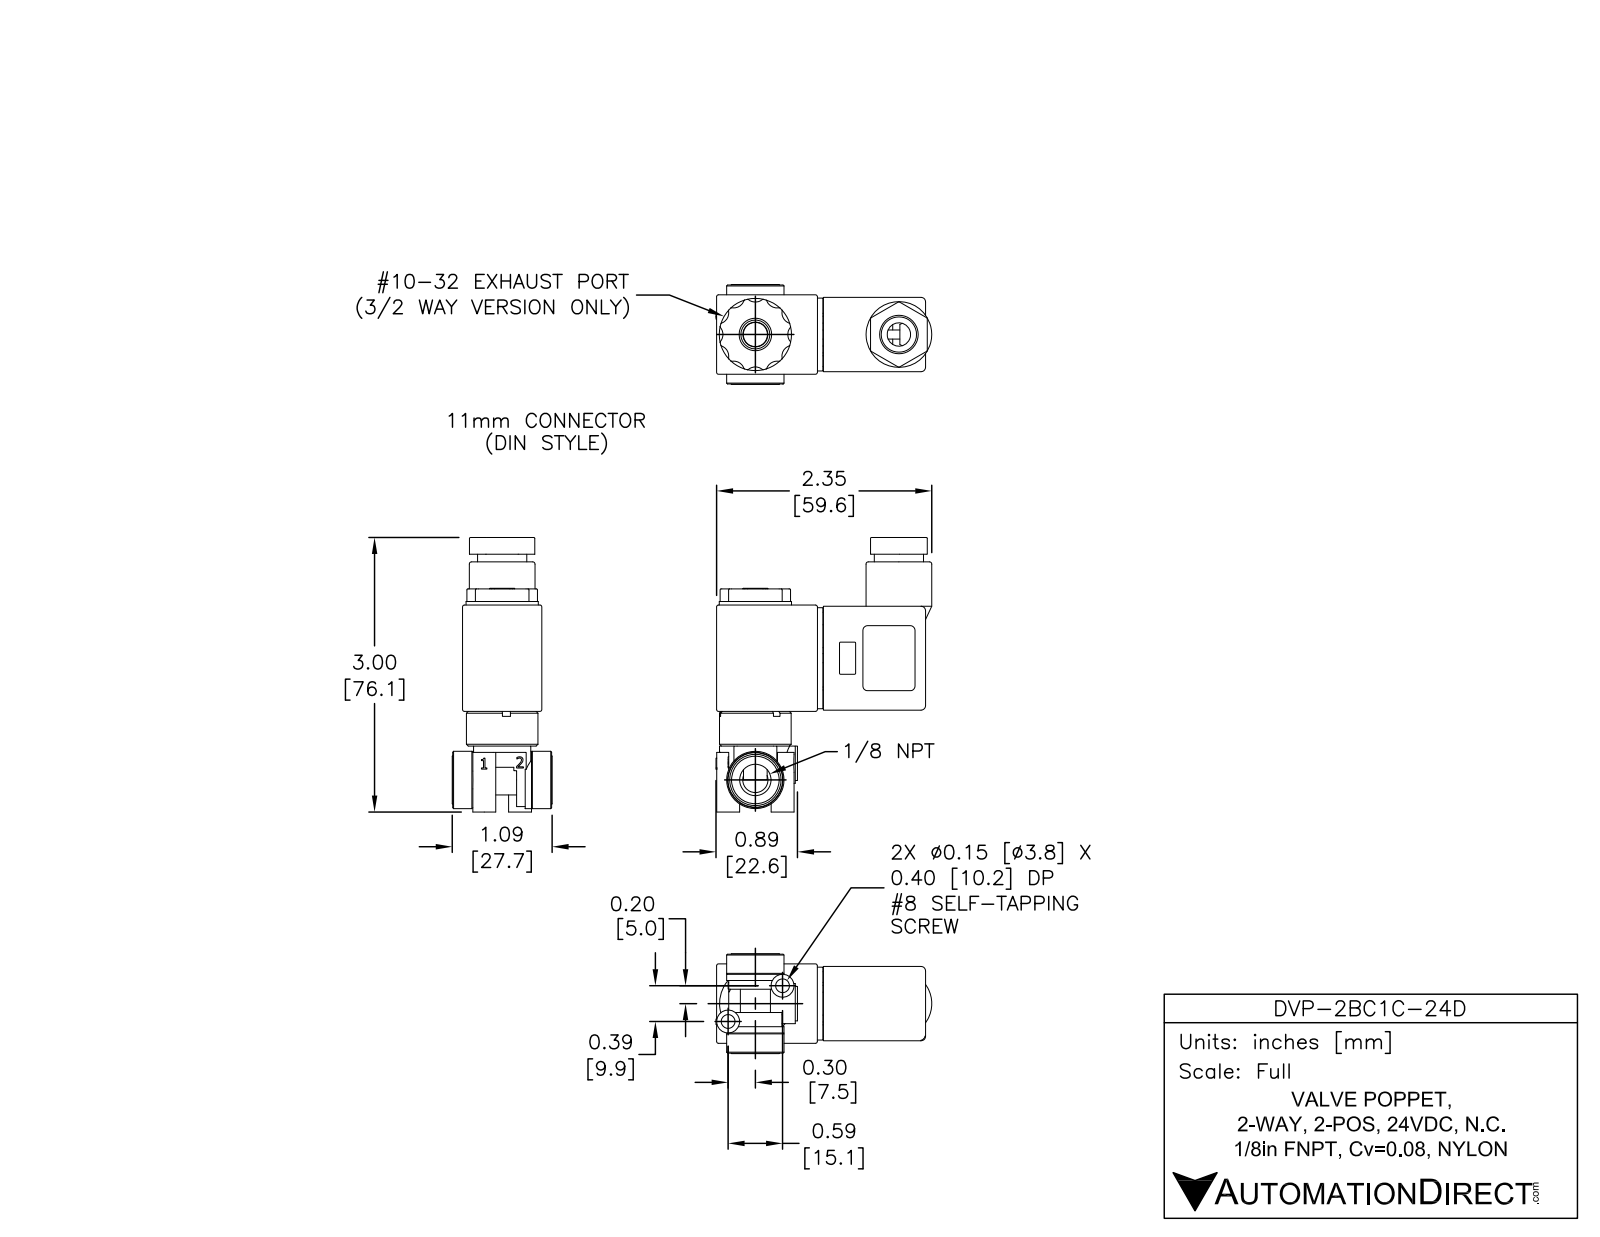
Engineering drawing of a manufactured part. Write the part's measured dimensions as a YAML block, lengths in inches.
part_name: "DVP-2BC1C-24A"
step_written_by: "SolidWorks 2015 (AUTOMOTIVE_DESIGN)"
units: inches
bodies: {solids: 4, faces: 1335, planar: 683, cylindrical: 243, other: 409}
overall_size: [2.978, 2.354, 1.09]
volume: 1.977
surface_area: 32.53
round_holes:
  - {diameter: 0.1, count: 2}
  - {diameter: 0.125, count: 2}
  - {diameter: 0.15, count: 2}
  - {diameter: 0.062, count: 1}
  - {diameter: 0.102, count: 1}
  - {diameter: 0.165, count: 1}
  - {diameter: 0.204, count: 1}
  - {diameter: 0.268, count: 1}
  - {diameter: 0.272, count: 1}
  - {diameter: 0.275, count: 1}
  - {diameter: 0.276, count: 1}
  - {diameter: 0.321, count: 1}
round_bosses_or_shafts:
  - {diameter: 0.25, count: 3}
  - {diameter: 0.625, count: 2}
  - {diameter: 0.788, count: 1}
  - {diameter: 0.781, count: 1}
  - {diameter: 0.717, count: 1}
  - {diameter: 0.59, count: 1}
  - {diameter: 0.56, count: 1}
  - {diameter: 0.538, count: 1}
partial_cylinders:
  - {radius: 0.01, count: 46}
  - {radius: 0.05, count: 16}
  - {radius: 0.02, count: 12}
  - {radius: 0.121, count: 12}
  - {radius: 0.044, count: 3}
  - {radius: 0.024, count: 2}
  - {radius: 0.025, count: 2}
  - {radius: 0.028, count: 2}
face_to_face_distances: [0.06, 0.087, 0.779, 0.028, 0.839, 0.751, 0.866, 1.16, 0.037, 0.829]
hole_center_spacings: [0.355, 0.175, 0.23, 0.51, 0.57, 0.71, 0.726, 0.997]
